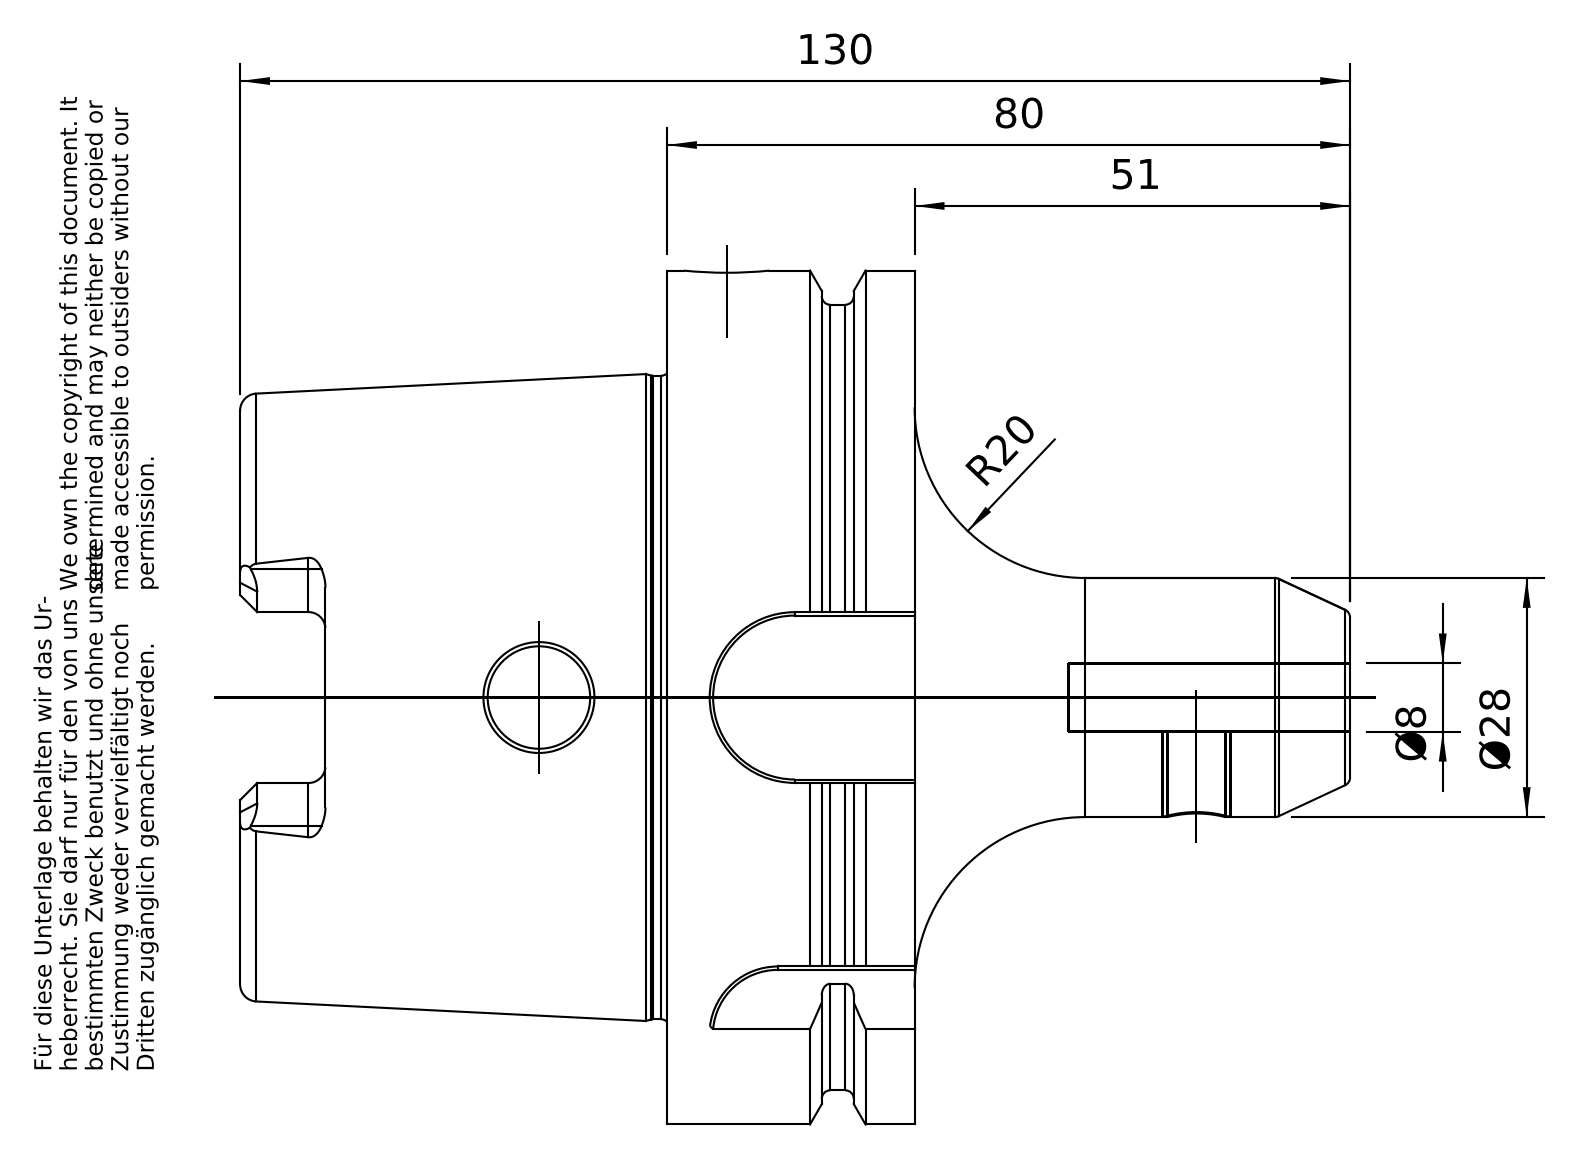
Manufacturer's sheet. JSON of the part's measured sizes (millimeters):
{"part_name": "A100-000-08", "step_written_by": "PRO/ENGINEER BY PARAMETRIC TECHNOLOGY CORPORATION, 2010430 (CONFIG_CONTROL_DESIGN)", "units": "millimeters", "bodies": {"solids": 1, "faces": 180, "planar": 50, "cylindrical": 55, "other": 75}, "overall_size": [130, 100, 100], "volume_mm3": 292171, "surface_area_mm2": 55053, "round_holes": [[8, 2], [6.8, 1], [10, 1], [12, 1], [22.5, 1], [24, 1], [24.32, 1], [24.5, 1], [53, 1], [63, 1]], "round_bosses_or_shafts": [[100, 1], [92, 1], [75.36, 1], [28, 1]], "partial_cylinders_radius": [[2, 6], [5, 4], [8, 1], [10, 1], [11, 1]], "face_to_face_distances": [29, 12.5, 16.5, 50, 62.5, 79, 88, 78.5, 28.5, 16], "hole_center_spacings": [55]}
